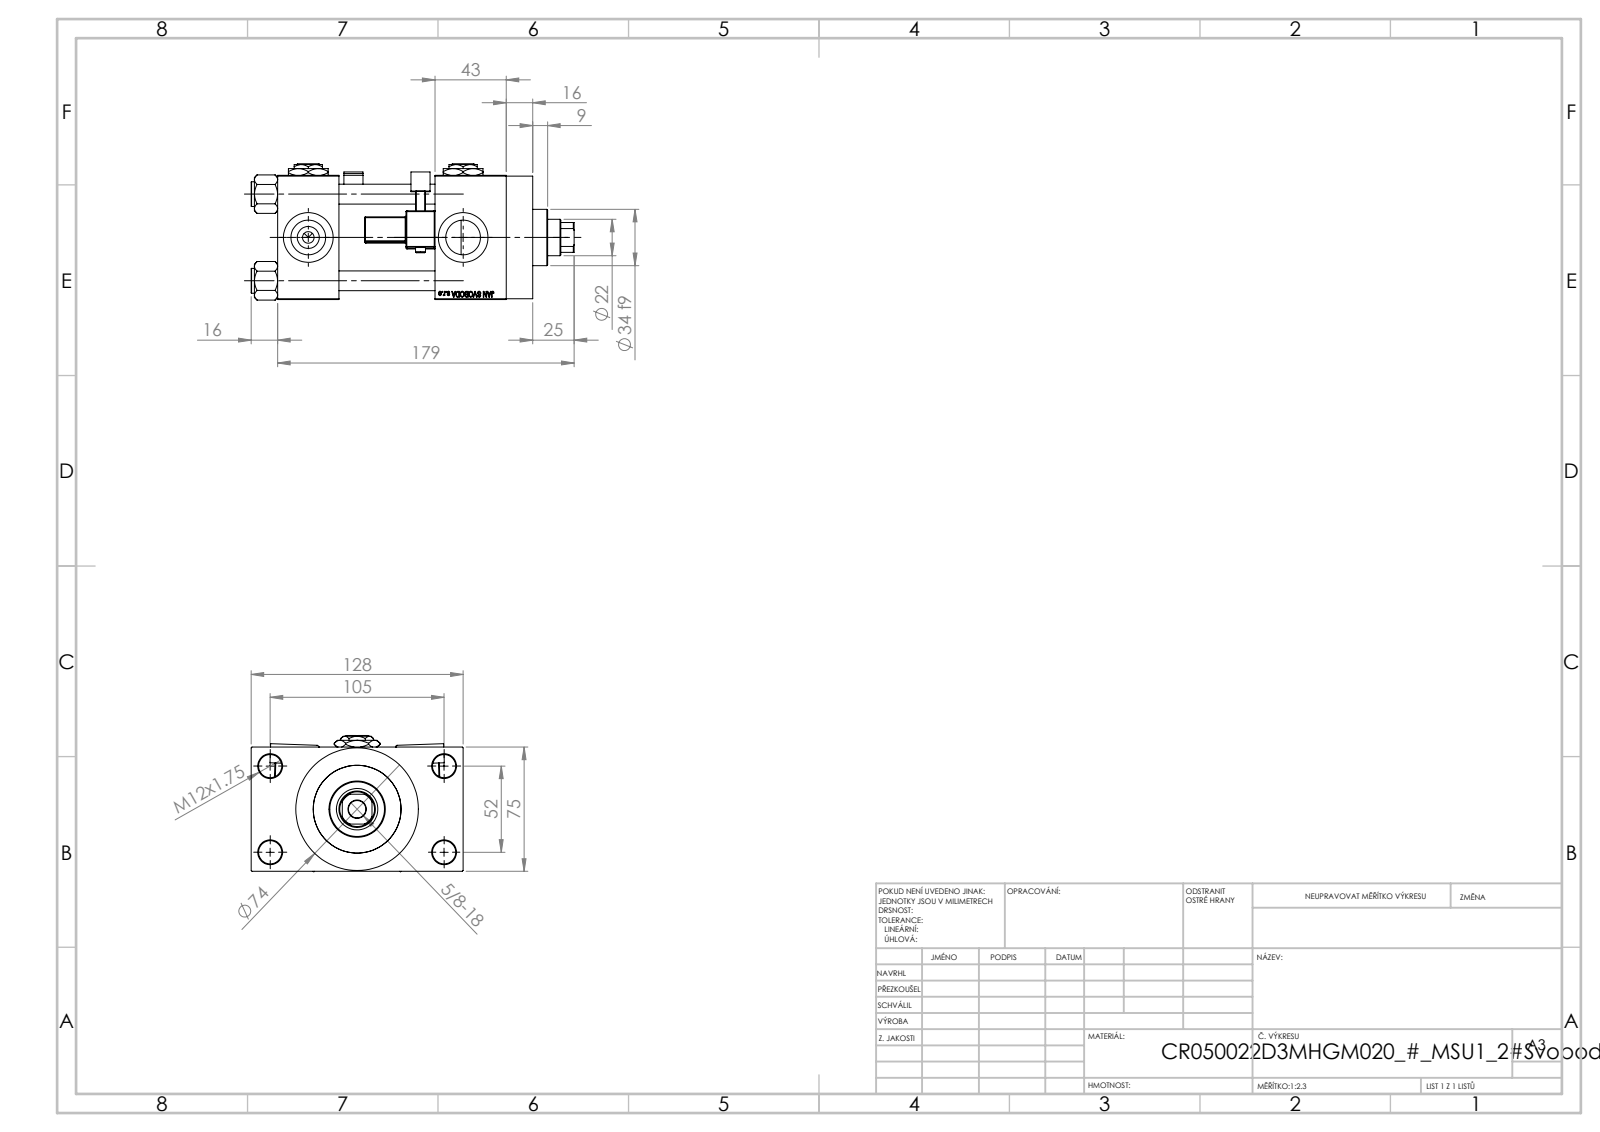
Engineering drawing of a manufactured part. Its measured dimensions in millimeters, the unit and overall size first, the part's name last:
Units: millimetres
Overall size (bounding box): 195 × 128 × 82.27
Round holes (diameter × count): ⌀12 ×4, ⌀14 ×4, ⌀20.96 ×4, ⌀30 ×4, ⌀7 ×3, ⌀10.5 ×1, ⌀22 ×1, ⌀25 ×1, ⌀41 ×1, ⌀50 ×1, ⌀53 ×1
Round bosses / shafts (diameter × count): ⌀15 ×4, ⌀6 ×2, ⌀74 ×1, ⌀56 ×1, ⌀34 ×1
Partial cylindrical surfaces — rounded edges, fillets, slot ends (radius × count): R0.5 ×48, R1 ×2, R2.5 ×2, R4 ×2, R10.5 ×1
Main face-to-face distances: 75, 58, 37, 95, 26.5, 101.5, 138, 101, 43, 16
Hole centre spacings: 26.35, 36.98, 52.3, 58.43, 58.59, 78.65, 94.37, 52
Volume: 834 279 mm³ · Surface area: 183 190 mm²
Bodies: 15 solids, 1358 faces (603 planar, 159 cylindrical, 596 other)
Part name (STEP PRODUCT): V215CR_VCP_D; NUT_M5_D; V215CR_D_TYCINKA; V215_VC_A (+3 more)
STEP written by: SolidWorks 2019 (CONFIG_CONTROL_DESIGN)
